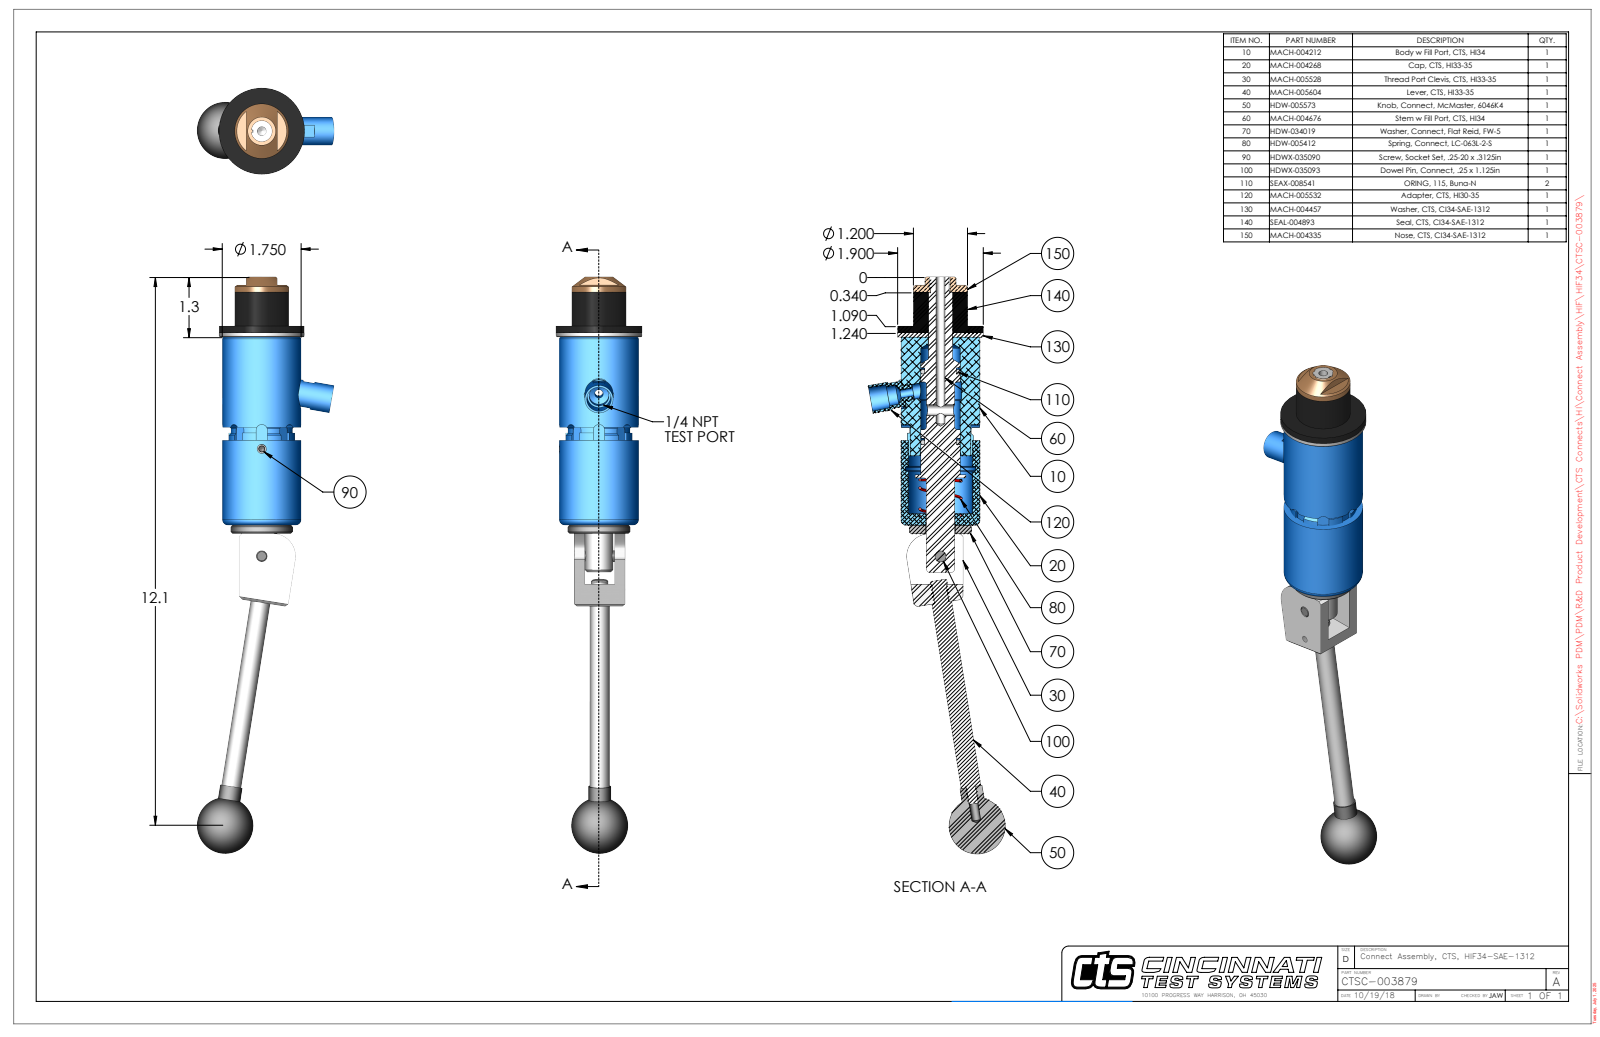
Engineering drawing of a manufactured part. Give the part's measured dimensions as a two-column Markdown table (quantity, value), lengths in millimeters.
| quantity | value |
| --- | --- |
| part name | CTSC-003879 |
| STEP written by | SolidWorks 2023 (AUTOMOTIVE_DESIGN) |
| units | millimeters |
| bodies | 9 solids, 328 faces (120 planar, 139 cylindrical, 69 other) |
| overall size | 324.4 × 77.3 × 48.3 |
| volume | 243 800 mm³ |
| surface area | 55 990 mm² |
| round holes (diameter × count) | 5.1 × 2, 3.8 × 1, 4.7 × 1, 5.2 × 1, 6.3 × 1, 6.4 × 1, 6.4 × 1, 8 × 1, 10.7 × 1, 11.1 × 1, 13.5 × 1, 13.7 × 1 |
| round bosses / shafts (diameter × count) | 12.7 × 2, 11.2 × 2, 6.4 × 2, 48.3 × 1, 44.5 × 1, 35.1 × 1, 30.5 × 1, 15.9 × 1 |
| partial cylindrical surfaces (radius × count) | 3.2 × 4, 0.7 × 2, 4.2 × 1, 4.2 × 1, 4.4 × 1, 8.4 × 1, 12.7 × 1, 17.7 × 1 |
| main face-to-face distances | 2.4, 108.2, 105.8, 22.9, 25.2, 131, 19.1, 3.8, 6.2, 112 |
| hole center spacings | 18.8, 60.4, 79.1 |
